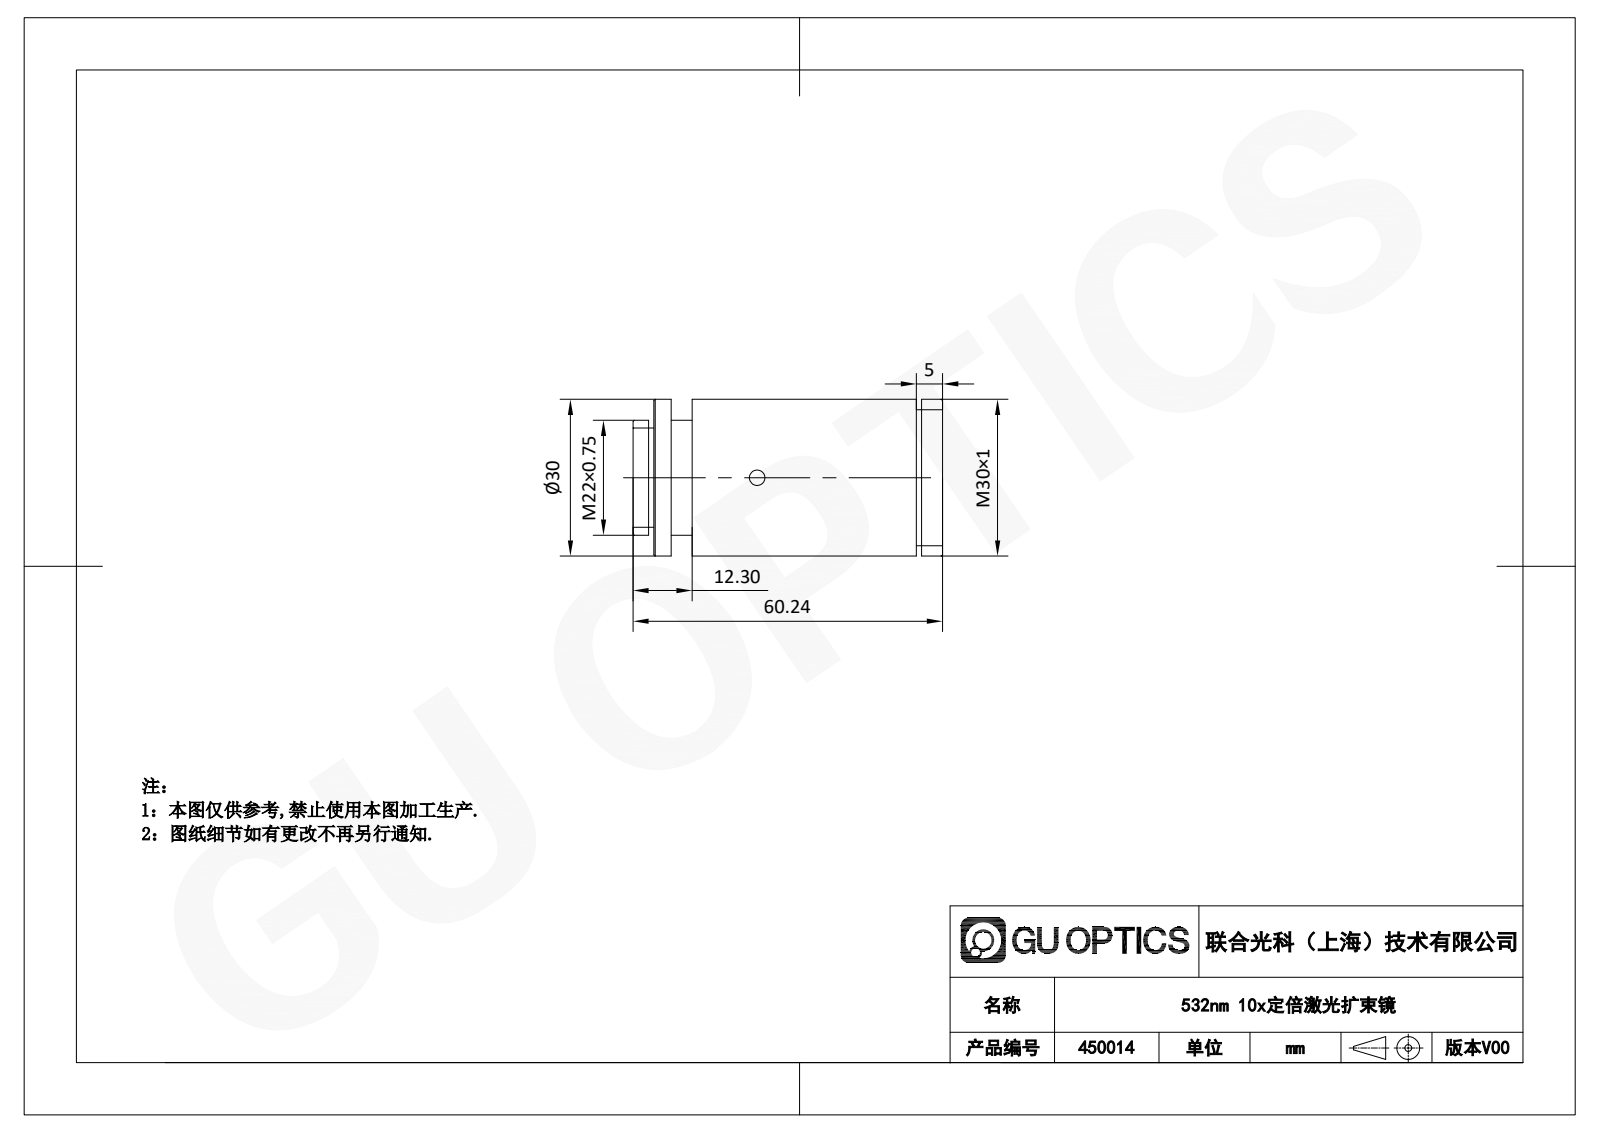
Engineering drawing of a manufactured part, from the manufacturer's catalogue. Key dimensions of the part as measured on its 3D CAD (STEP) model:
Part name (STEP PRODUCT): 450014
STEP written by: SolidWorks 2020 (AUTOMOTIVE_DESIGN)
Units: millimetres
Bodies: 1 solid, 43 faces (11 planar, 22 cylindrical, 10 other)
Overall size (bounding box): 60.24 × 30 × 30
Volume: 32 436 mm³ · Surface area: 10 706 mm²
Round holes (diameter × count): ⌀8 ×1, ⌀18 ×1
Round bosses / shafts (diameter × count): ⌀30 ×1, ⌀26 ×1, ⌀22 ×1, ⌀19 ×1
Main face-to-face distances: 4, 56.24, 47.94, 8.3, 52.24, 4.3, 51.94, 43.94, 1, 12.3
